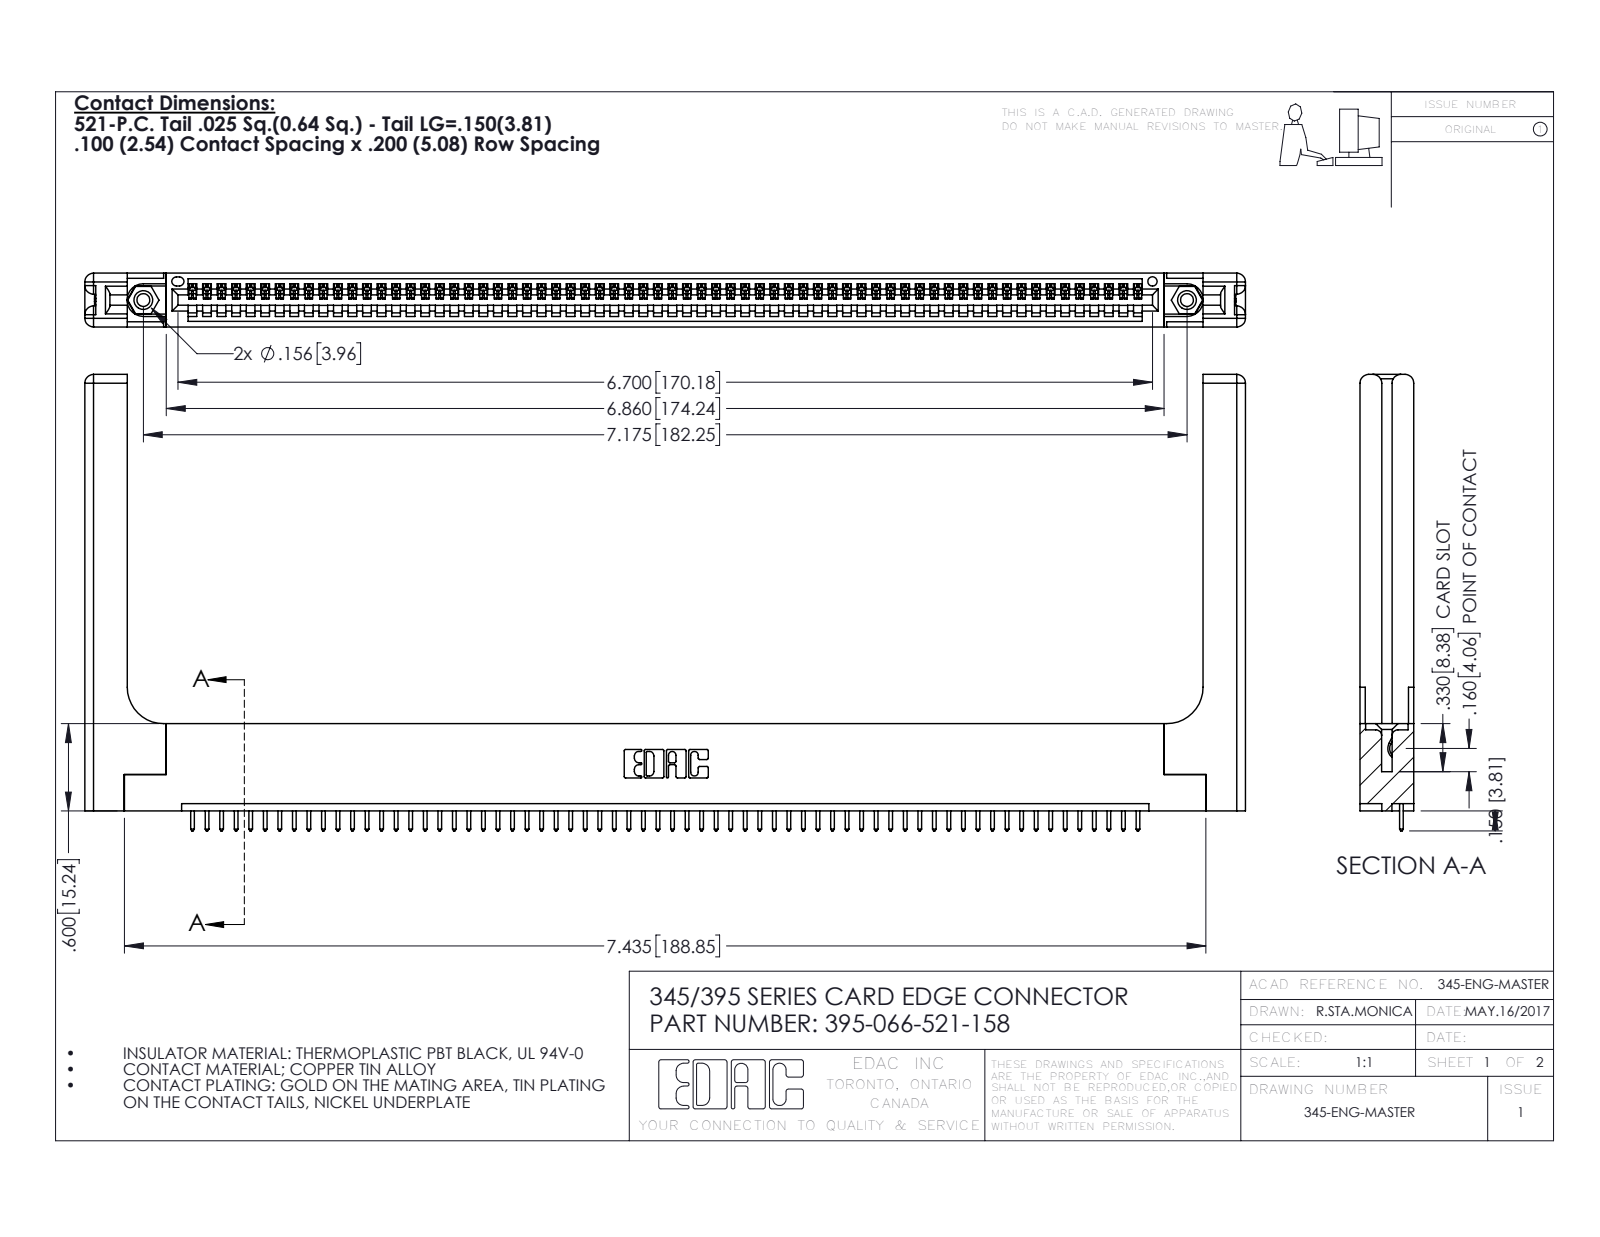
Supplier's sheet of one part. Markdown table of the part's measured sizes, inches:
| quantity | value |
| --- | --- |
| part name | 345 Part_Flush Mounting Lugs - 0.156 Dia-TH; 395-066-521-158; 345-220-058_345-220-058; 345-250-001_345-250-001-102 (+1 more) |
| STEP written by | SolidWorks 2016 (CONFIG_CONTROL_DESIGN) |
| units | inches |
| bodies | 71 solids, 4210 faces (2868 planar, 1282 cylindrical, 60 other) |
| overall size | 7.979 × 3.137 × 0.37 |
| volume | 1.694 in³ |
| surface area | 47.26 in² |
| round holes (diameter × count) | 0.089 × 2, 0.125 × 2, 0.156 × 2, 0.064 × 1 |
| round bosses / shafts (diameter × count) | 0.155 × 2 |
| partial cylindrical surfaces (radius × count) | 0.006 × 132, 0.01 × 132, 0.01 × 22, 0.06 × 16, 0.007 × 6, 0.031 × 6, 0.026 × 3, 0.03 × 2 |
| main face-to-face distances | 0.072, 0.37, 0.298, 0.2, 0.098, 0.272, 0.025, 0.225, 0.148, 0.15 |
| hole center spacings | 0.27, 6.939, 7.175 |
